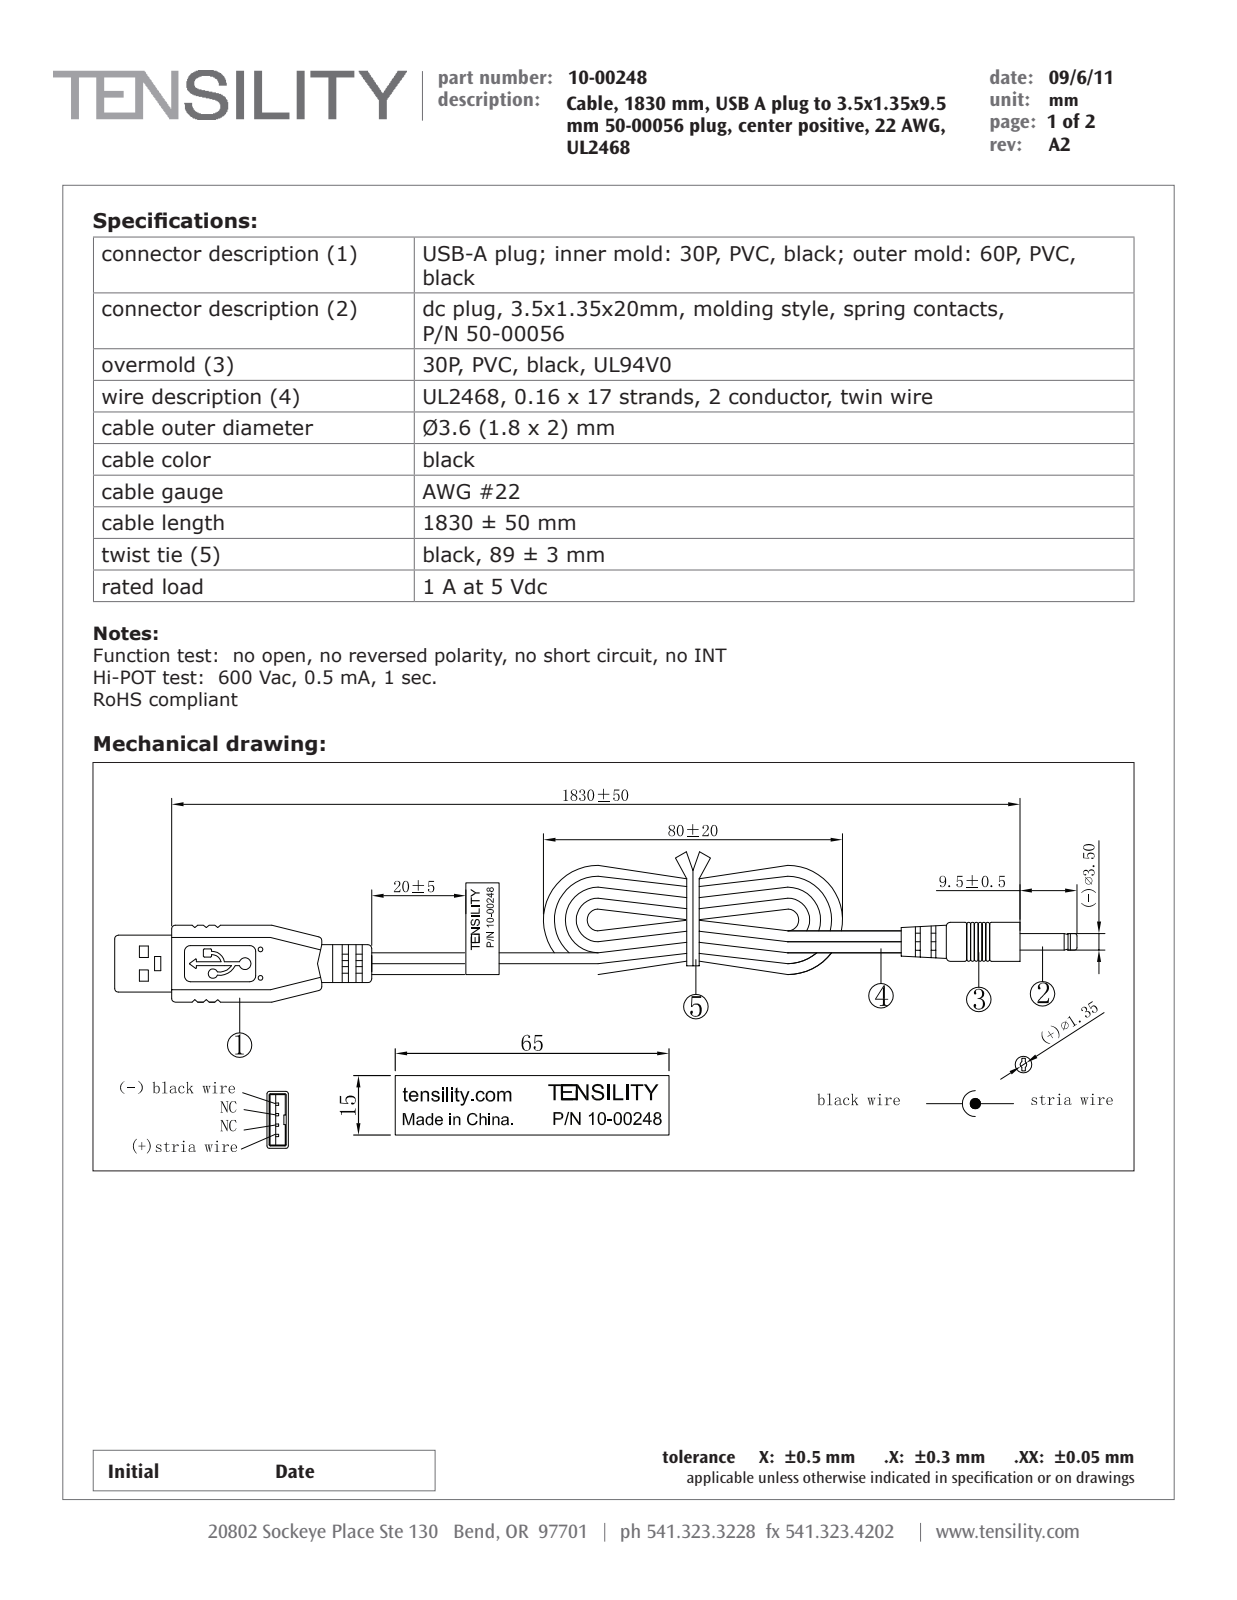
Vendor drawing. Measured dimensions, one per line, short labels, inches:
name: 50-00056 insulator; 24-00050_default; 30-00008_wbc; 50-00056 shell (+8 more)
written by: SolidWorks 2015 (AUTOMOTIVE_DESIGN)
unit: in
bodies: 59 solids, 1162 faces (586 planar, 286 cylindrical, 290 other)
size: 8.813 × 1.522 × 0.331
volume: 0.435 in³; area: 19.73 in²
holes: 2× ⌀0.033, 1× ⌀0.047, 1× ⌀0.053, 1× ⌀0.059, 1× ⌀0.071, 1× ⌀0.114, 1× ⌀0.138, 1× ⌀0.15
bosses: 2× ⌀0.075, 1× ⌀0.315, 1× ⌀0.286, 1× ⌀0.283, 1× ⌀0.177, 1× ⌀0.165, 1× ⌀0.157, 1× ⌀0.142
rounds: 32× R0.004, 11× R0.02, 10× R0.006, 8× R0.008, 8× R0.03, 4× R0.012, 4× R0.025, 4× R0.051
face distances: 0.077, 0.073, 0.071, 0.079, 0.254, 0.092, 0.152, 0.081, 0.177, 0.169
hole spacings: 0.035, 0.034, 0.036, 0.07
